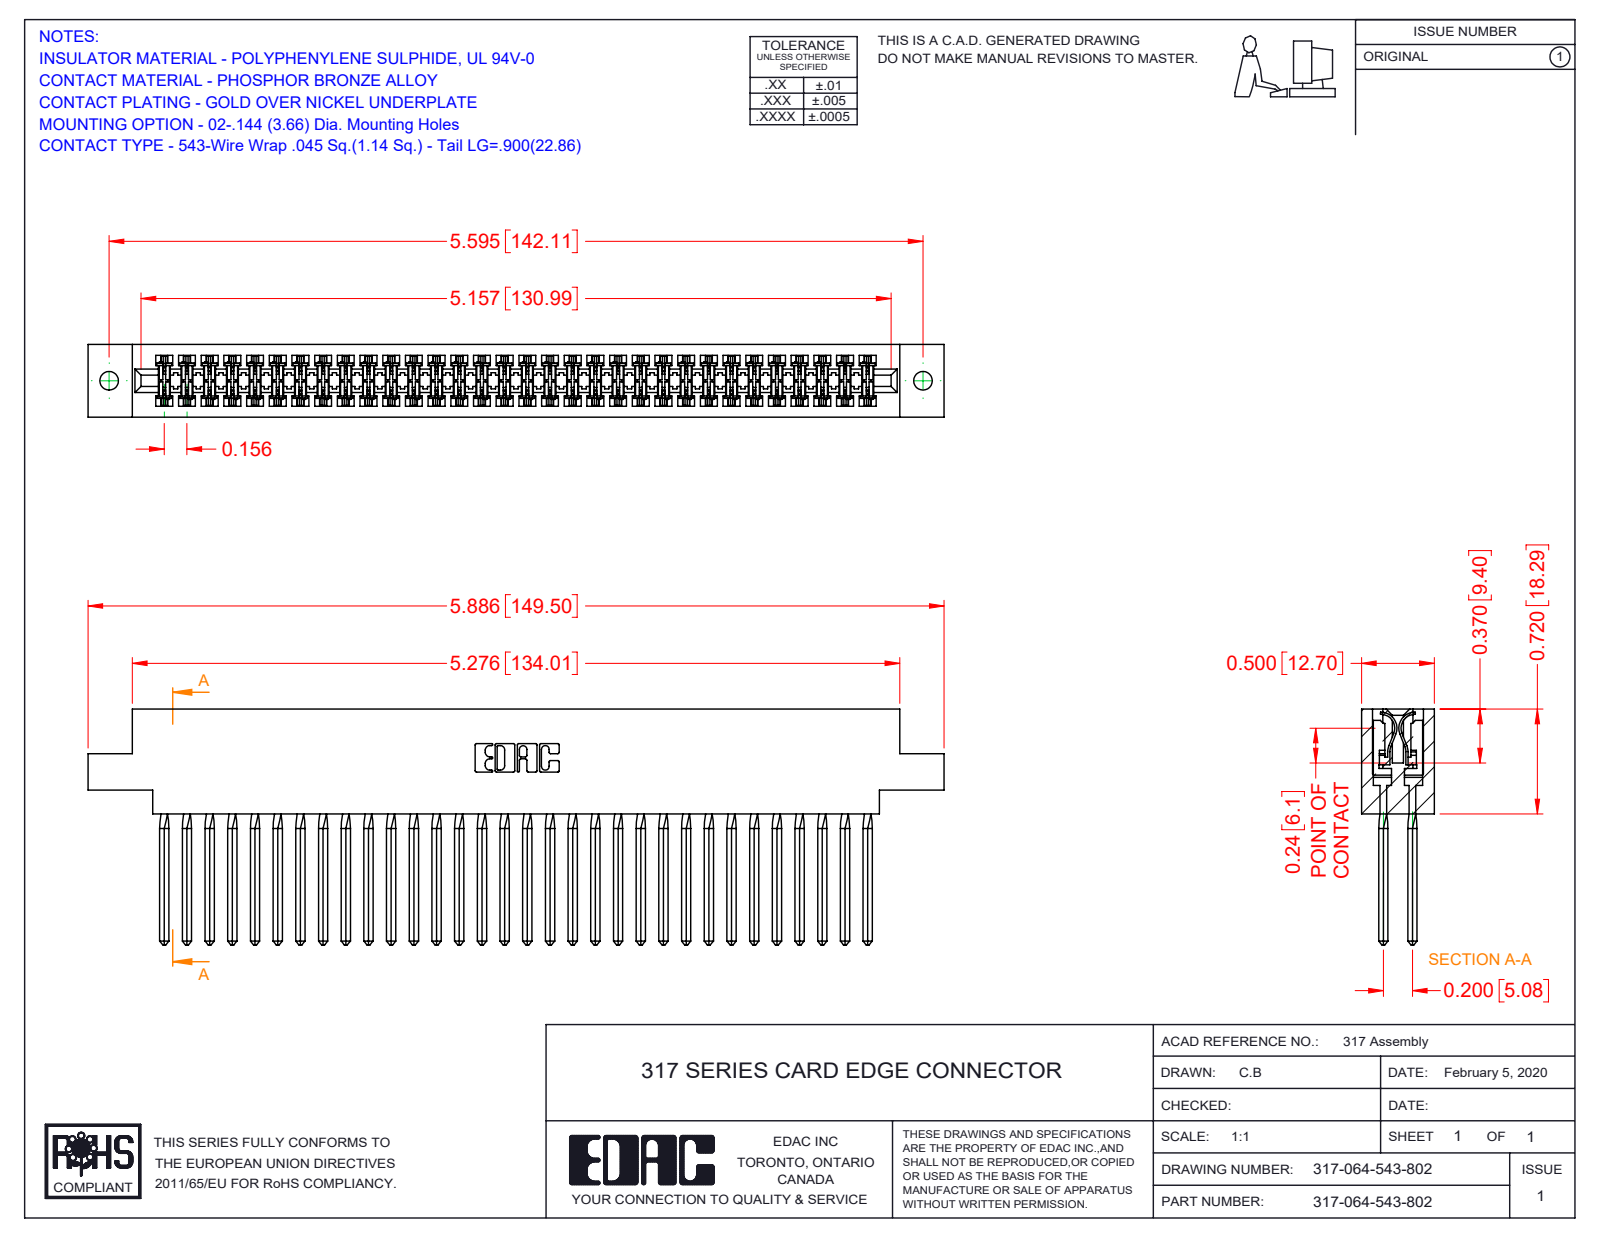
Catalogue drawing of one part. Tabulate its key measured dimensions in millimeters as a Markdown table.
| quantity | value |
| --- | --- |
| part name | 317 Part_.144 Dia; 317-290-001_543; 317-064-543-802 |
| STEP written by | SolidWorks 2016 (CONFIG_CONTROL_DESIGN) |
| units | millimeters |
| bodies | 65 solids, 5798 faces (4730 planar, 812 cylindrical, 256 other) |
| overall size | 149.5 × 41.1 × 12.7 |
| volume | 25 040 mm³ |
| surface area | 37 320 mm² |
| round holes (diameter × count) | 3.3 × 2 |
| partial cylindrical surfaces (radius × count) | 0.4 × 128, 0.3 × 22, 0.2 × 6, 0.8 × 6, 0.7 × 3, 2.4 × 2, 2.5 × 2, 2.8 × 2 |
| main face-to-face distances | 12.7, 1.9, 10.8, 8.9, 2.8, 5, 2.4, 5.1, 2.9, 3.3 |
| hole center spacings | 142.1 |
